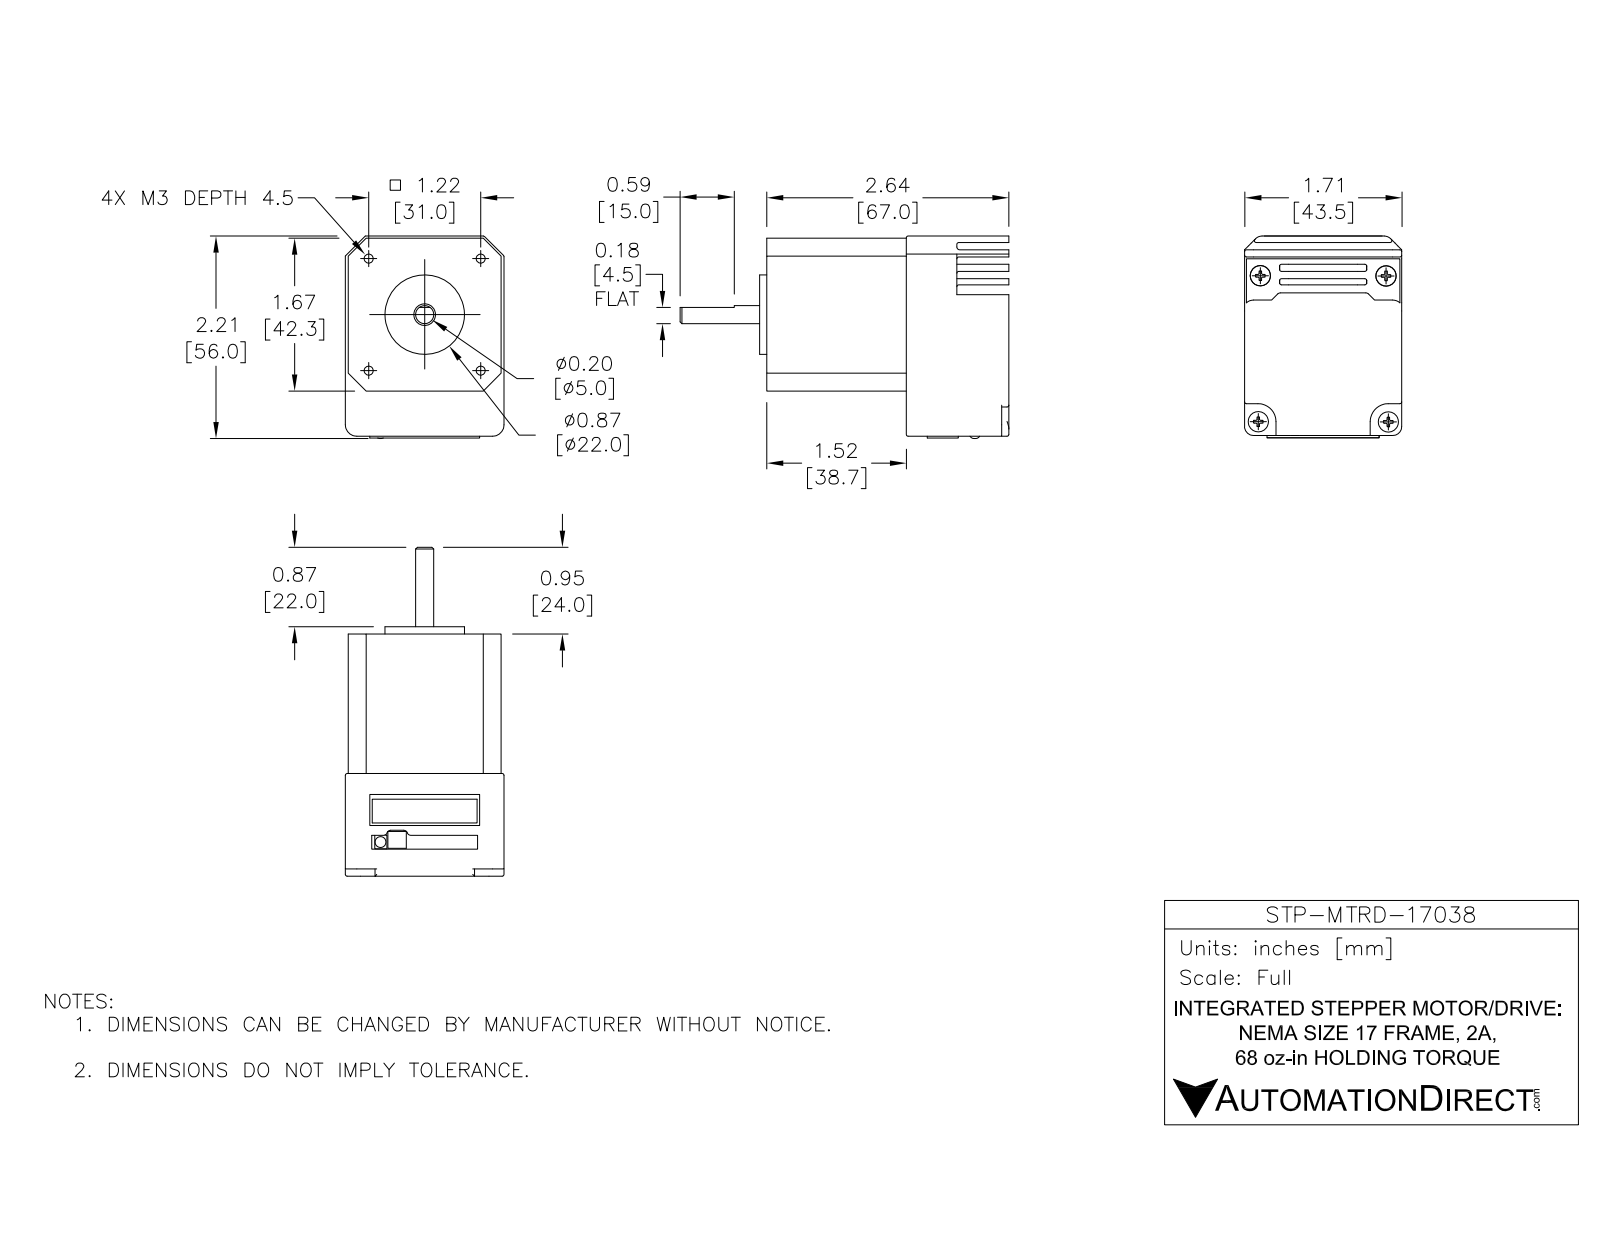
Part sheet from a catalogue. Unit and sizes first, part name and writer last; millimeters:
Units: millimetres
Overall size (bounding box): 91 × 56.39 × 43.9
Round holes (diameter × count): ⌀2.5 ×6, ⌀7.5 ×1, ⌀15 ×1
Round bosses / shafts (diameter × count): ⌀5.6 ×2, ⌀22 ×1, ⌀5 ×1, ⌀3 ×1
Partial cylindrical surfaces — rounded edges, fillets, slot ends (radius × count): R0.5 ×85, R1 ×6, R2.5 ×6, R0.68 ×4, R10.96 ×4, R25.37 ×4, R3 ×2, R3.16 ×2
Main face-to-face distances: 2, 41.9, 39.9, 67, 4, 43.9, 6, 1.71, 41.61, 10
Hole centre spacings: 21.92, 31, 14.24, 34.48, 36.11, 43.84, 45.12, 56.01
Volume: 123 671 mm³ · Surface area: 20 387 mm²
Bodies: 1 solid, 396 faces (146 planar, 161 cylindrical, 89 other)
Part name (STEP PRODUCT): STP-MTRD-17038
STEP written by: SolidWorks 2017 (AUTOMOTIVE_DESIGN)
